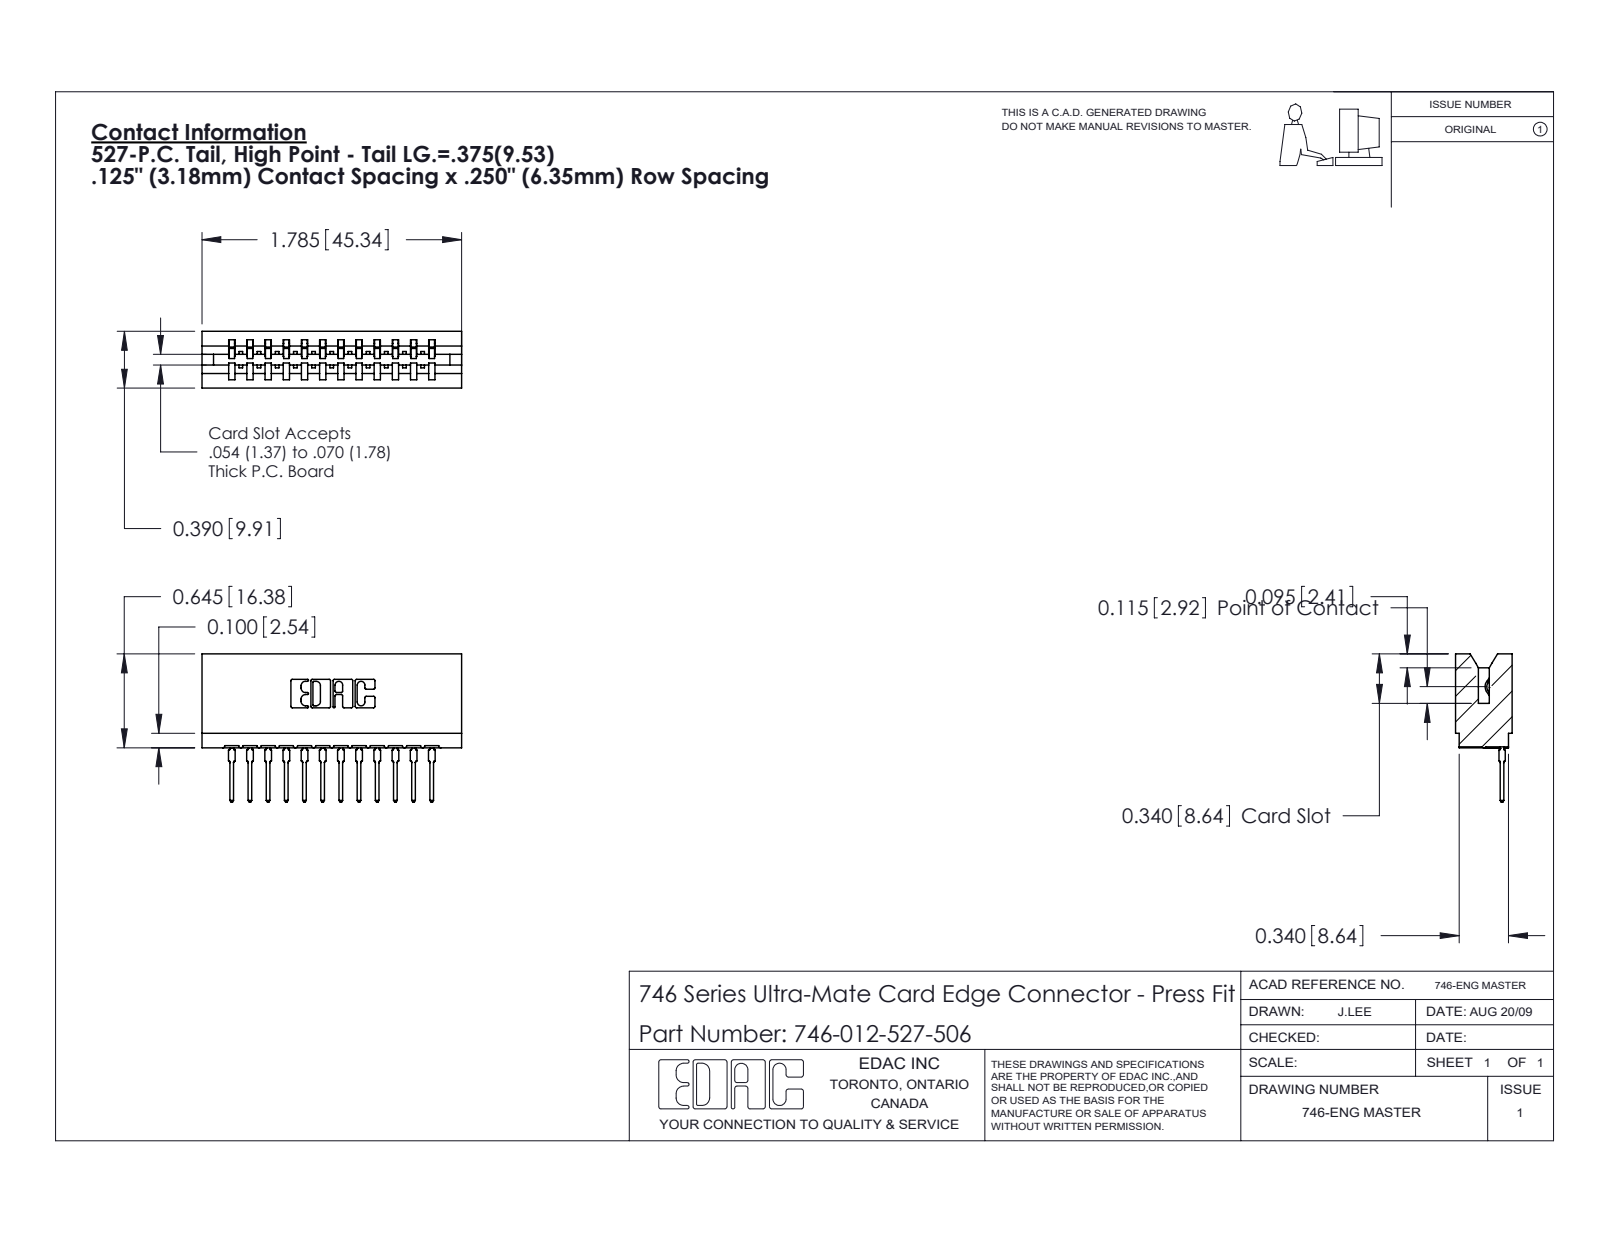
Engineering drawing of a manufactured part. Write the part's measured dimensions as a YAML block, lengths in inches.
part_name: "746-012-527-506; 746 Part_.340 Slot Depth - 06; 746-292-001_527"
step_written_by: "SolidWorks 2020 (CONFIG_CONTROL_DESIGN)"
units: inches
bodies: {solids: 13, faces: 1394, planar: 812, cylindrical: 270, other: 312}
overall_size: [1.785, 1.019, 0.39]
volume: 0.321
surface_area: 10.41
partial_cylinders:
  - {radius: 0.021, count: 24}
  - {radius: 0.01, count: 22}
  - {radius: 0.015, count: 13}
  - {radius: 0.007, count: 6}
  - {radius: 0.031, count: 6}
  - {radius: 0.005, count: 4}
  - {radius: 0.011, count: 4}
  - {radius: 0.026, count: 3}
face_to_face_distances: [0.25, 0.5, 0.057, 0.333, 0.125, 0.39, 0.042, 0.125, 0.292, 0.542]
